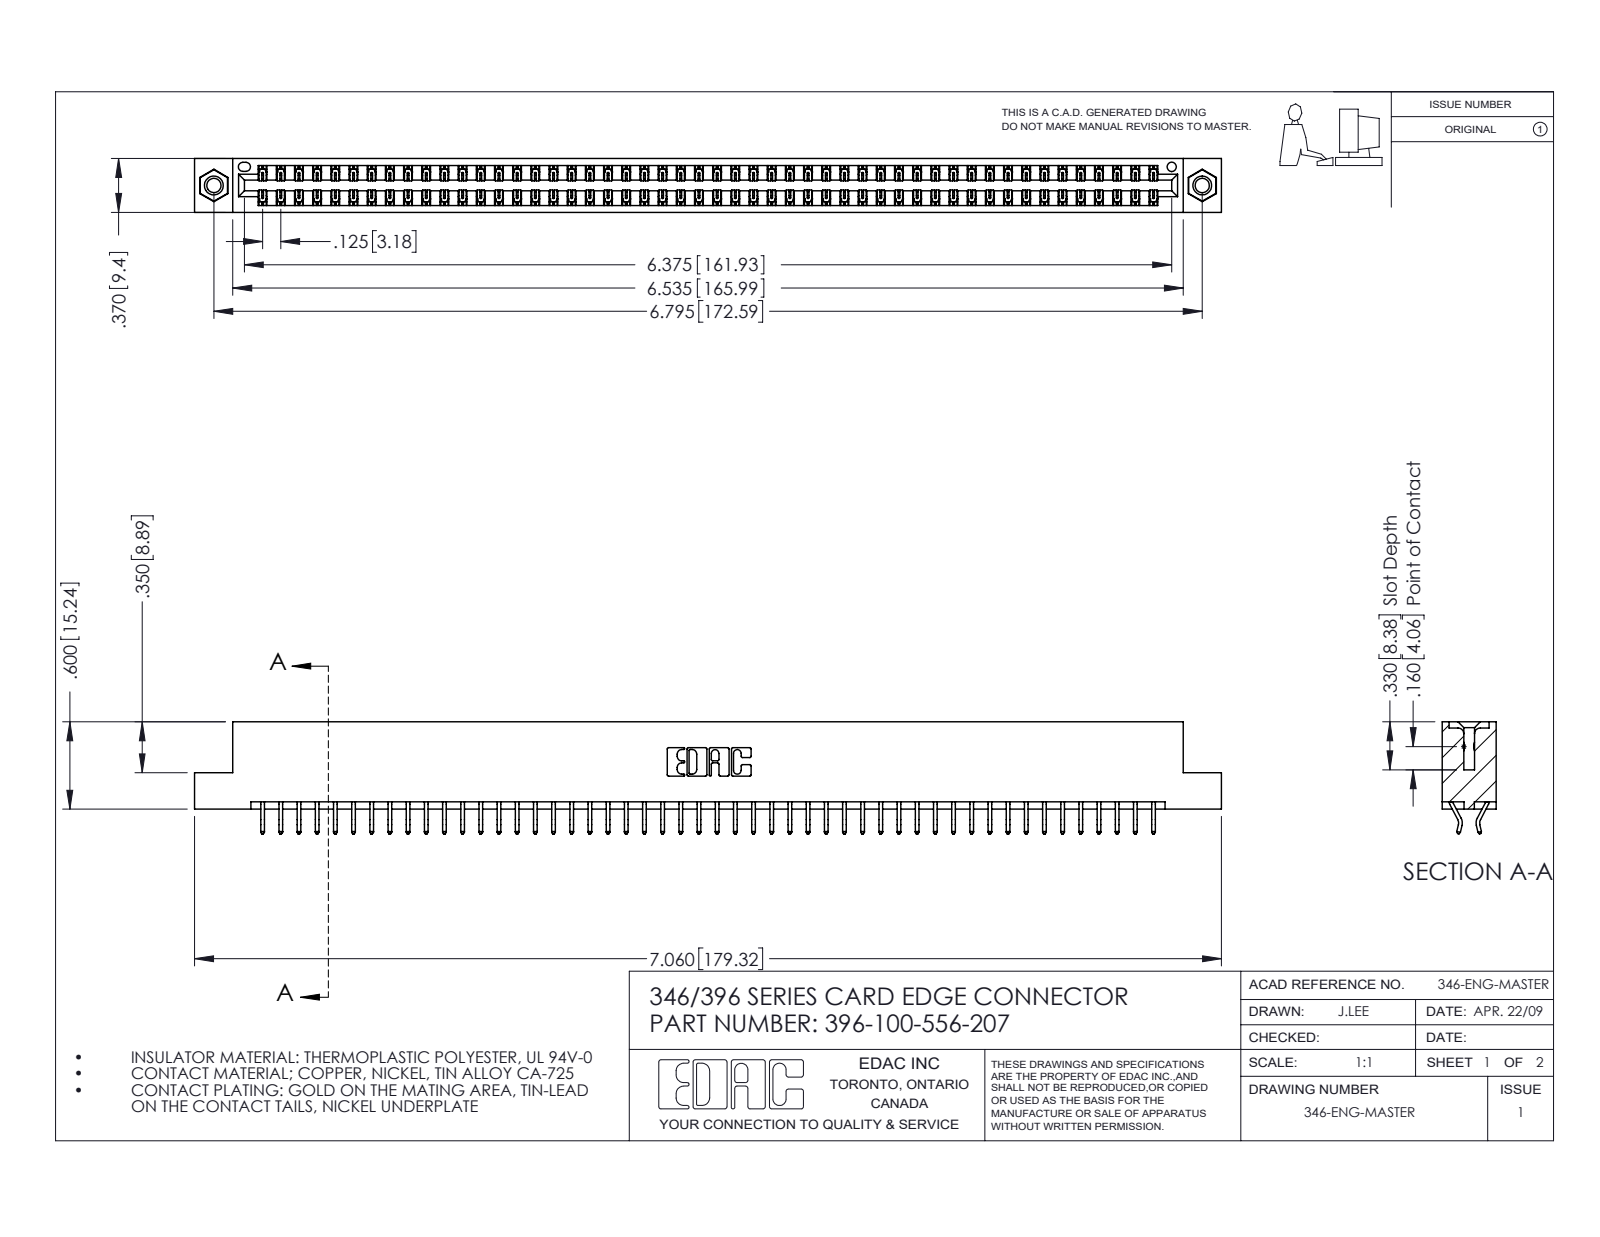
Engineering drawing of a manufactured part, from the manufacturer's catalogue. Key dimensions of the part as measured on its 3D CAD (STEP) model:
Part name (STEP PRODUCT): 396-100-556-207; 345-292-001_556 Tail; 345-250-001_345-250-005-103; 346 Part_Flush Mounting Lugs - 0.156 Dia-TI
STEP written by: SolidWorks 2016 (CONFIG_CONTROL_DESIGN)
Units: inches
Bodies: 103 solids, 5982 faces (4008 planar, 1958 cylindrical, 16 other)
Overall size (bounding box): 7.06 × 0.77 × 0.37
Volume: 1.07 in³ · Surface area: 37.45 in²
Round holes (diameter × count): ⌀0.098 ×2, ⌀0.125 ×2, ⌀0.156 ×2, ⌀0.064 ×1
Round bosses / shafts (diameter × count): ⌀0.155 ×2
Partial cylindrical surfaces — rounded edges, fillets, slot ends (radius × count): R0.006 ×150, R0.01 ×22, R0.007 ×6, R0.031 ×6, R0.026 ×3, R0.01 ×2, R0.014 ×2, R0.022 ×2
Main face-to-face distances: 0.048, 0.322, 0.37, 0.25, 0.025, 0.072, 0.298, 0.275, 0.148, 0.222
Hole centre spacings: 0.246, 6.586, 6.795
